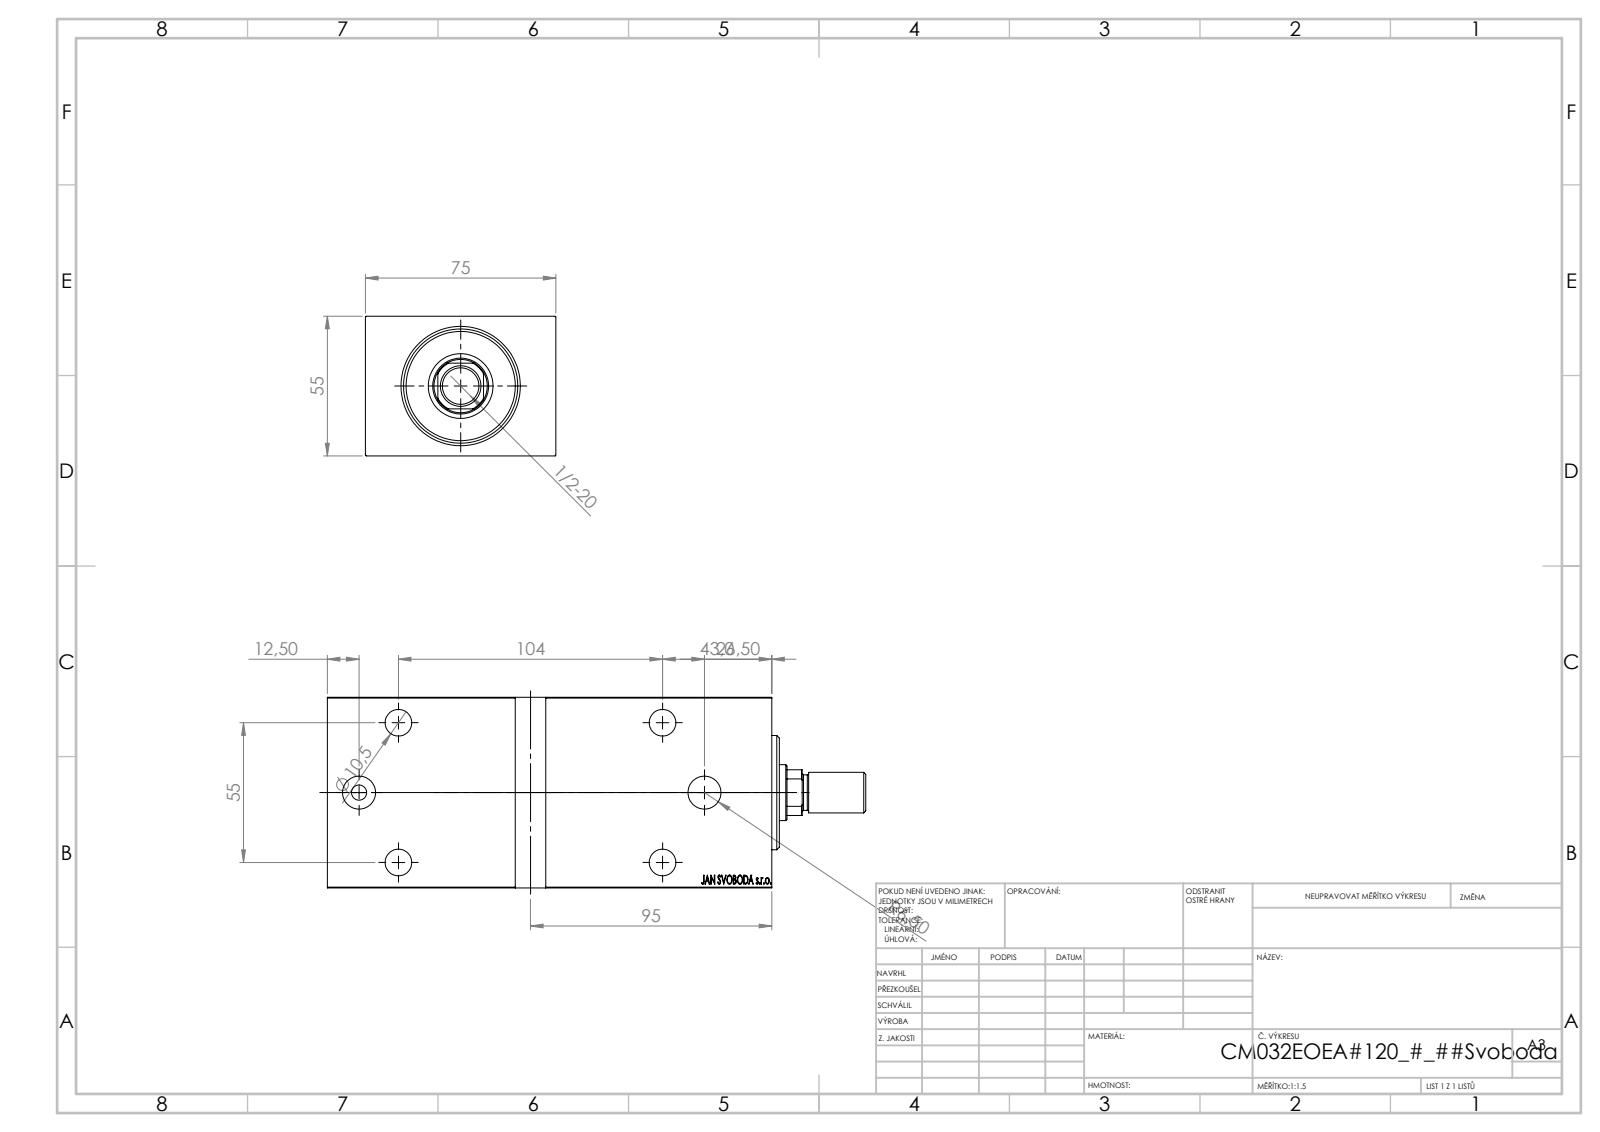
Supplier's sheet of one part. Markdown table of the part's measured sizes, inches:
| quantity | value |
| --- | --- |
| part name | V450CM_VC_B; V450CM_E_Body; V450CM_E_VCP; V450CM_MALE_METRIC |
| STEP written by | SolidWorks 2019 (CONFIG_CONTROL_DESIGN) |
| units | inches |
| bodies | 4 solids, 859 faces (411 planar, 48 cylindrical, 400 other) |
| overall size | 8.346 × 2.953 × 2.165 |
| volume | 39.95 in³ |
| surface area | 157.9 in² |
| round holes (diameter × count) | 0.413 × 5, 0.65 × 4, 0.512 × 2, 0.866 × 1, 1.004 × 1, 1.26 × 1, 1.772 × 1 |
| round bosses / shafts (diameter × count) | 1.339 × 1, 0.63 × 1, 0.551 × 1, 0.236 × 1 |
| partial cylindrical surfaces (radius × count) | 0.413 × 1 |
| main face-to-face distances | 2.165, 2.953, 6.89, 0.118, 0.394, 6.496, 0.197, 6.693, 6.299, 7.008 |
| hole center spacings | 1.243, 1.263, 2.165, 4.094, 4.632, 4.828, 4.866, 5.354 |
